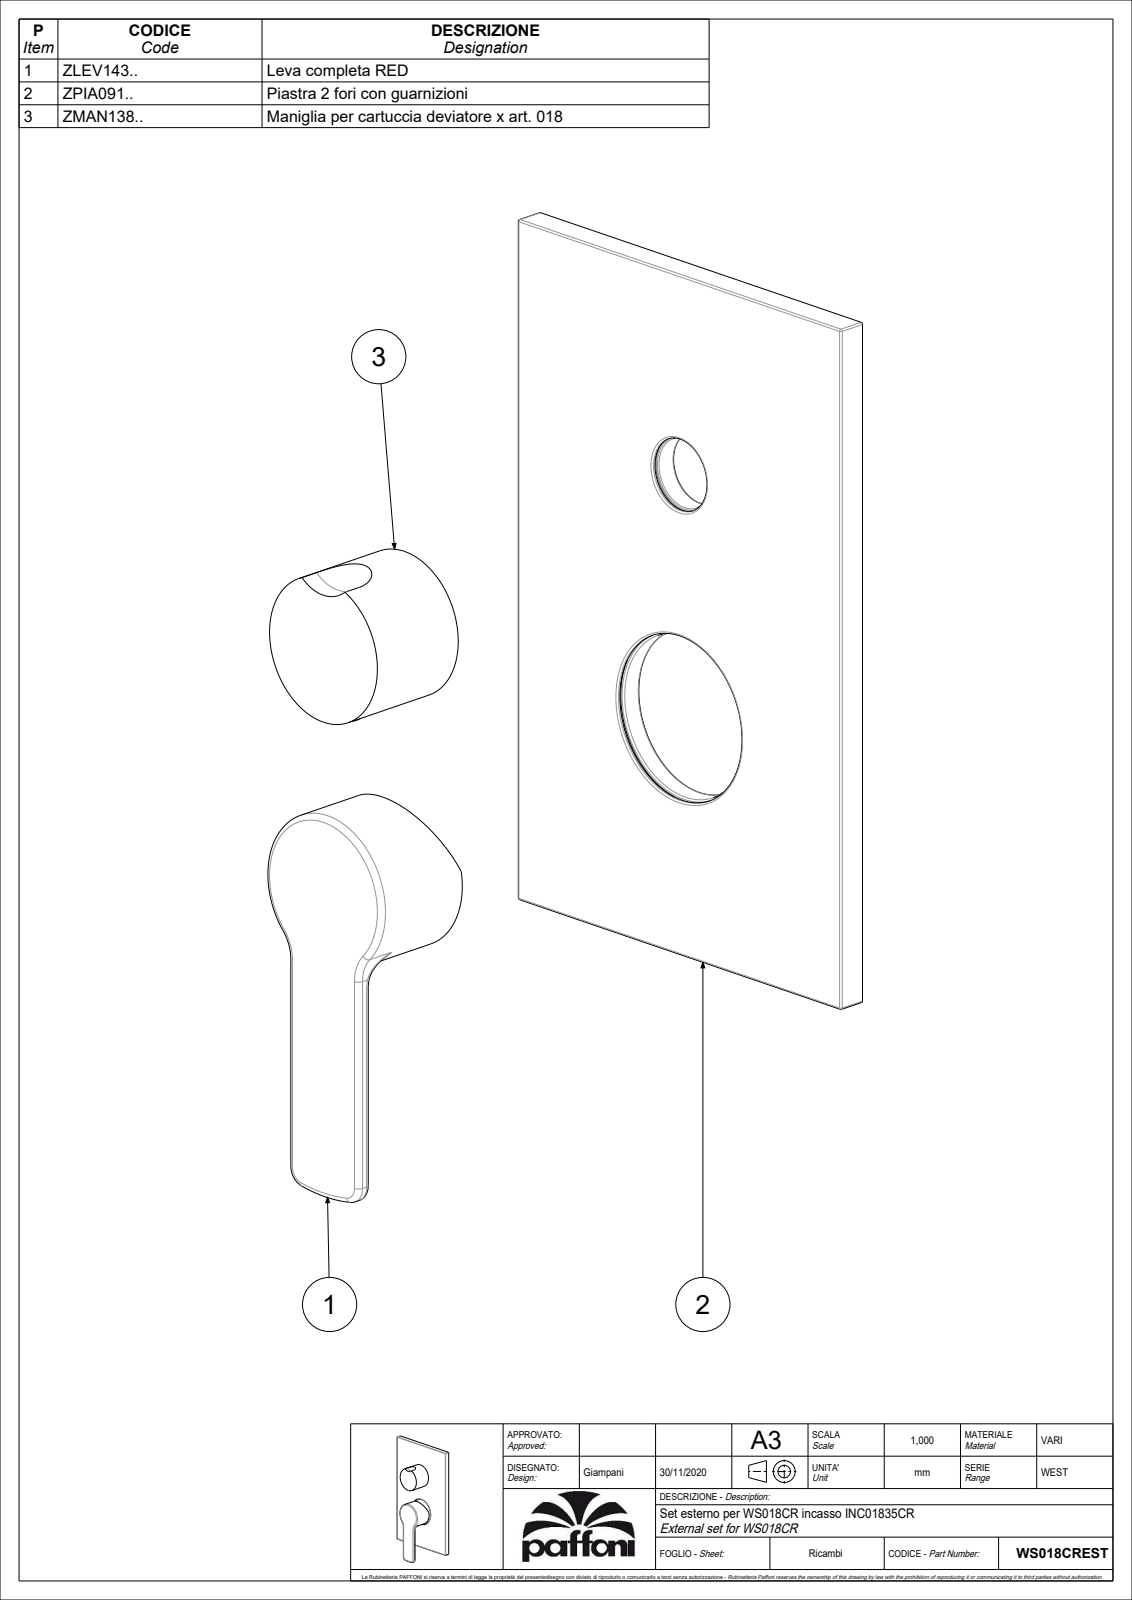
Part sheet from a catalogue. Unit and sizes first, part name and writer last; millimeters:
Units: millimetres
Overall size (bounding box): 209 × 120 × 40.35
Round holes (diameter × count): ⌀3 ×2, ⌀3.2 ×1, ⌀3.3 ×1, ⌀4.2 ×1, ⌀4.5 ×1, ⌀14.8 ×1, ⌀19.2 ×1, ⌀20 ×1, ⌀21 ×1, ⌀23.2 ×1, ⌀36 ×1, ⌀45 ×1
Round bosses / shafts (diameter × count): ⌀7.6 ×2, ⌀5.5 ×2, ⌀51 ×1, ⌀49 ×1, ⌀43 ×1, ⌀40 ×1, ⌀25 ×1, ⌀24 ×1
Partial cylindrical surfaces — rounded edges, fillets, slot ends (radius × count): R0.5 ×47, R1 ×8, R1.5 ×4, R5 ×2, R10 ×2, R12.5 ×1, R50 ×1
Main face-to-face distances: 2.5, 8, 5.5, 0.5, 5, 3, 30, 22.5, 27.5, 35.5
Hole centre spacings: 6, 10, 68, 78
Volume: 160 304 mm³ · Surface area: 100 959 mm²
Bodies: 3 solids, 396 faces (116 planar, 144 cylindrical, 136 other)
Part name (STEP PRODUCT): WS018CREST
STEP written by: CREO PARAMETRIC BY PTC INC, 2020044 (CONFIG_CONTROL_DESIGN)
